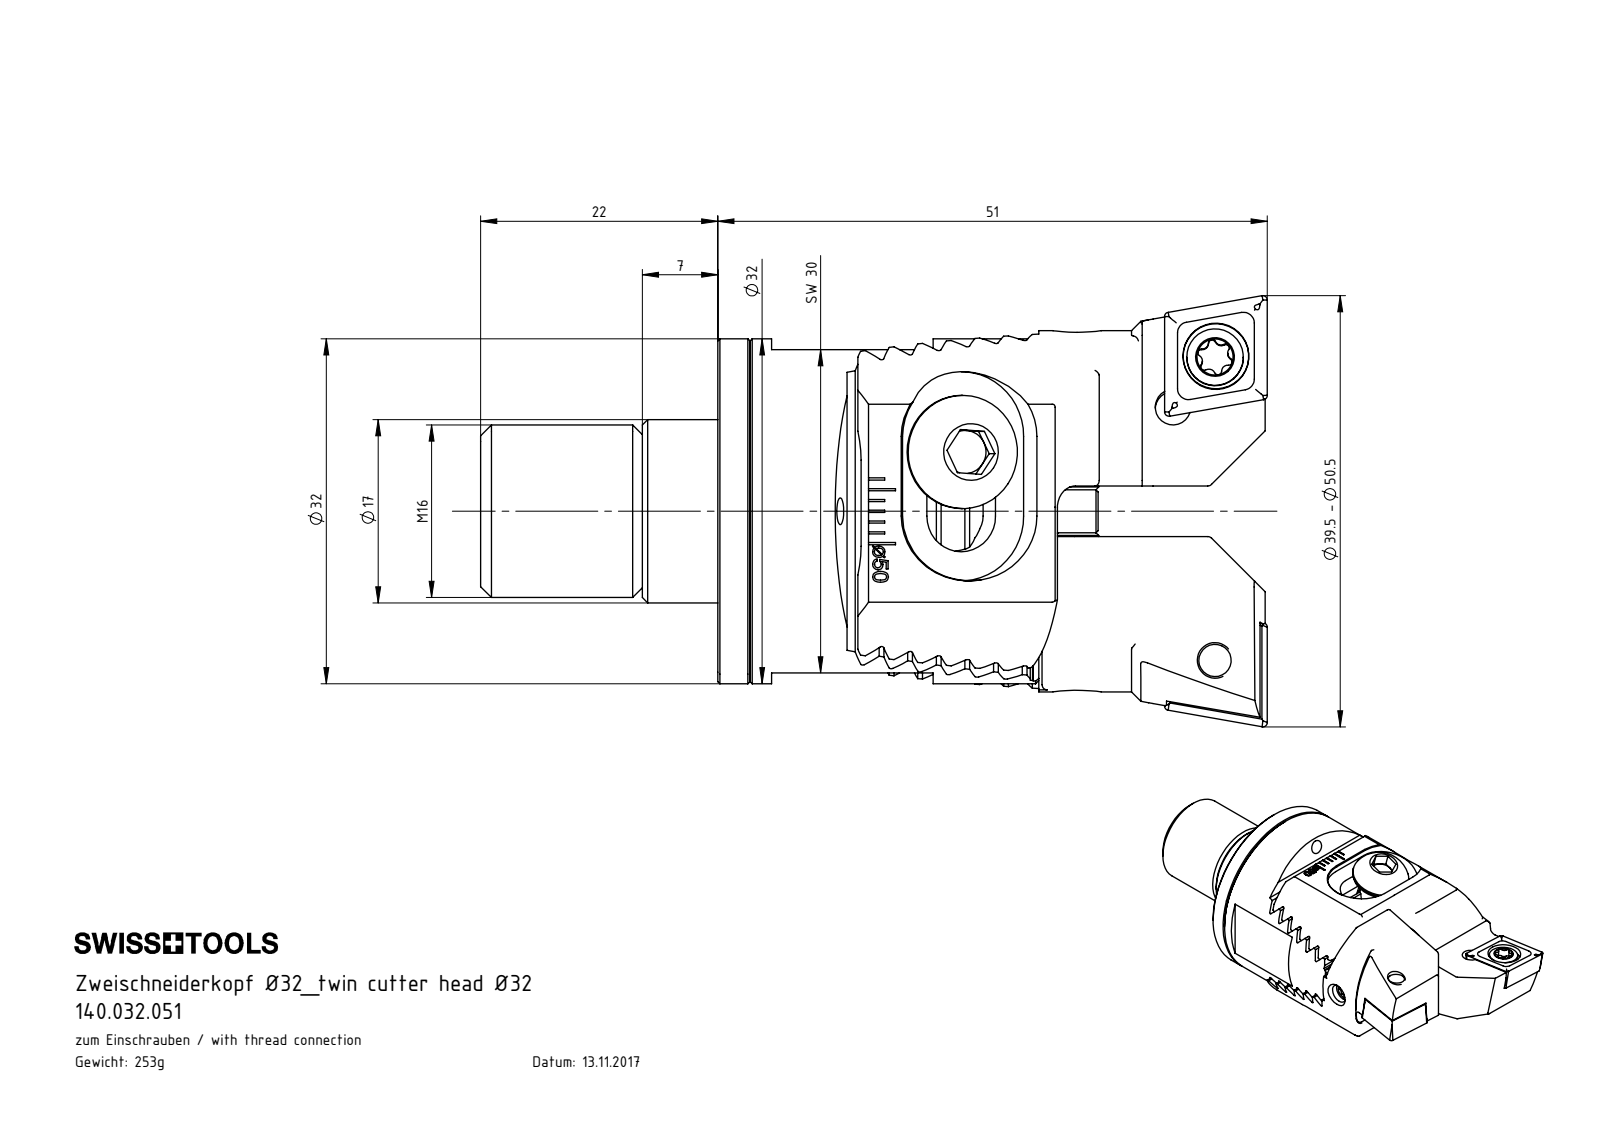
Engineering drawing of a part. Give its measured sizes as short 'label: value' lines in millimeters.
name: HP5-Z32.040.051_A; Z32-xxx.001.021_B; WCB-ER2.001.009_A; Z32-ER1.002.016_A (+8 more)
written by: SolidWorks 2017 (CONFIG_CONTROL_DESIGN)
unit: mm
bodies: 16 solids, 985 faces (457 planar, 232 cylindrical, 296 other)
size: 73 × 40 × 32
volume: 32 202 mm³; area: 19 598 mm²
holes: 5× ⌀2.5, 5× ⌀3.3, 2× ⌀1.6, 2× ⌀2, 2× ⌀4.4, 2× ⌀5, 2× ⌀6.1, 2× ⌀6.4, 2× ⌀6.8, 1× ⌀3.5, 1× ⌀10.2, 1× ⌀12.5
bosses: 4× ⌀4, 2× ⌀10.5, 2× ⌀10.2, 2× ⌀6, 2× ⌀5.25, 1× ⌀32, 1× ⌀16, 1× ⌀12
rounds: 16× R0.5, 14× R0.2, 12× R0.2, 12× R0.34, 12× R0.59, 4× R2, 4× R3.3, 4× R6
face distances: 2.38, 4.76, 7.14, 3, 9.52, 9.53, 4.89, 11.91, 7.15, 2.43
hole spacings: 6.07, 6.19, 24.22, 24.33, 28.65, 9, 9.01, 17.39
